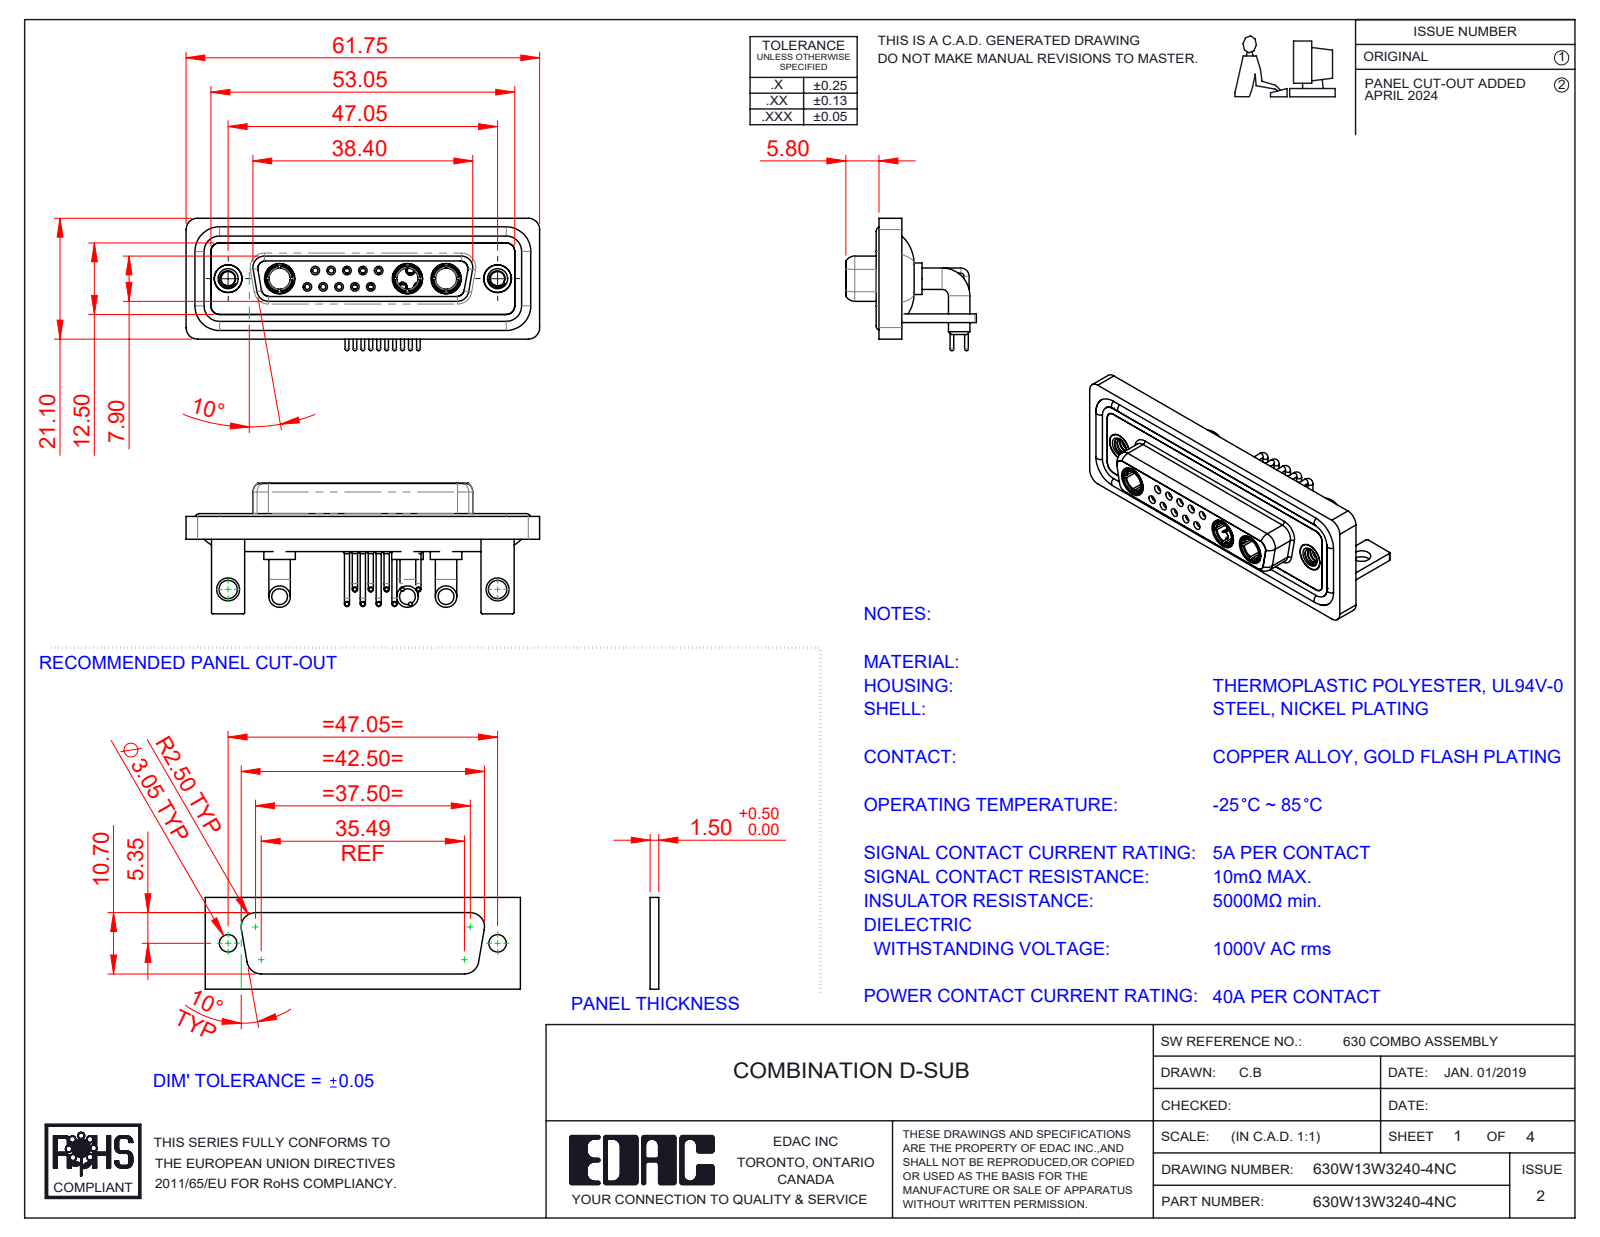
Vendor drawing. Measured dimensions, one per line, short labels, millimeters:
name: Power Socket_40A RA; 630Combo Contact Row 2_50 Contacts; 630Combo Stabilizer Bracket_50 Contacts; 630Combo Housing_13W3 (+6 more)
written by: SolidWorks 2023 (CONFIG_CONTROL_DESIGN)
unit: mm
bodies: 25 solids, 1192 faces (362 planar, 515 cylindrical, 315 other)
size: 61.75 × 23.12 × 22.8
volume: 9 048 mm³; area: 15 166 mm²
holes: 10× ⌀0.9, 10× ⌀1.1, 10× ⌀1.5, 10× ⌀2, 5× ⌀1.6, 5× ⌀1.7, 5× ⌀4.85, 3× ⌀3.7, 3× ⌀5.3, 2× ⌀2.5, 2× ⌀3.2, 2× ⌀4
bosses: 15× ⌀0.9, 12× ⌀1.6, 10× ⌀0.65, 6× ⌀3.75, 5× ⌀2, 5× ⌀1.5, 3× ⌀5.5, 3× ⌀5.2
rounds: 19× R2, 18× R1.5, 16× R0.25, 8× R1.35, 8× R1.6, 5× R0.5, 4× R0.6, 4× R0.65
face distances: 0.4, 1.8, 2.9, 3.7, 1.5, 4.1, 1.1, 1.4, 1.6, 3.1
hole spacings: 3.16, 2.77, 5.54, 5.04, 8.31, 5.03, 7.49, 11.08
